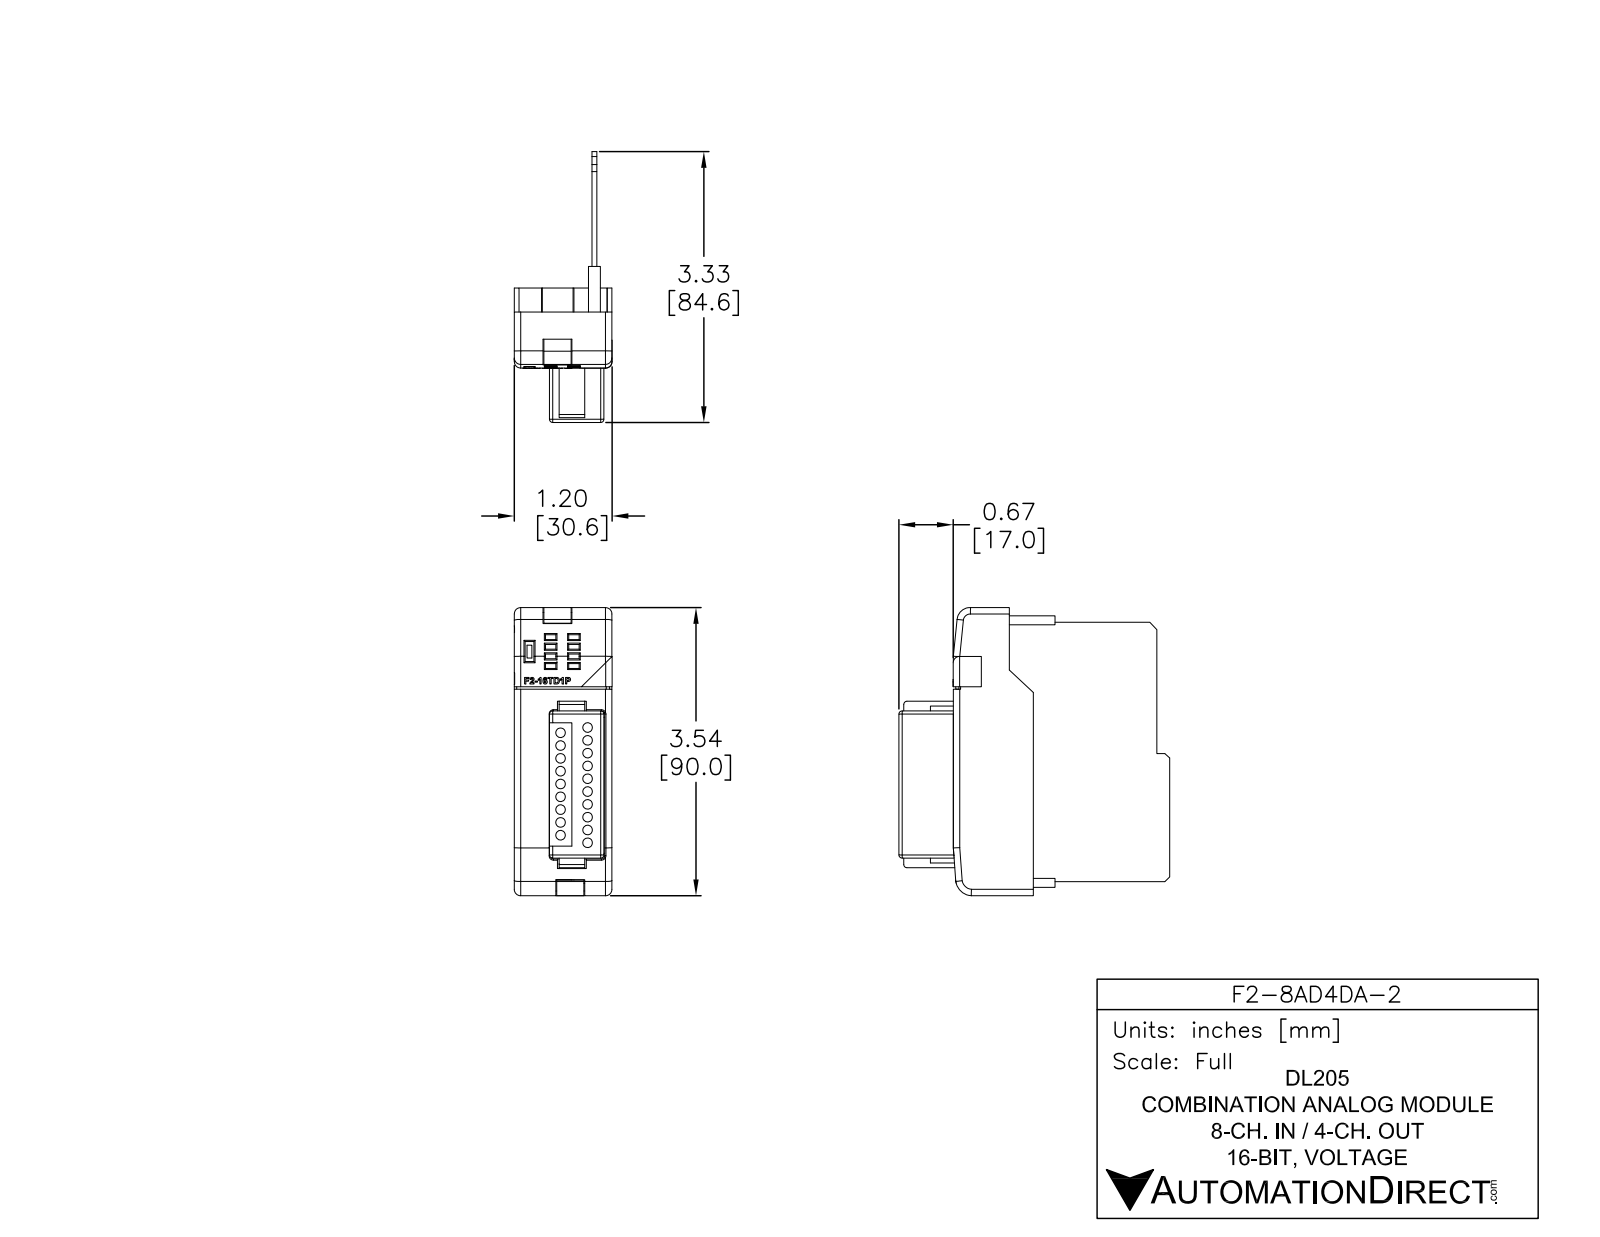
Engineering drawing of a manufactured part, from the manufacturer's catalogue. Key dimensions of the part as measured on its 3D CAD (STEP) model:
Part name (STEP PRODUCT): F2-8AD4DA-2
STEP written by: SolidWorks 2011 (AUTOMOTIVE_DESIGN)
Units: millimetres
Bodies: 2 solids, 618 faces (410 planar, 138 cylindrical, 70 other)
Overall size (bounding box): 90 × 84.6 × 30.55
Volume: 30 556 mm³ · Surface area: 32 608 mm²
Round holes (diameter × count): ⌀3 ×19
Partial cylindrical surfaces — rounded edges, fillets, slot ends (radius × count): R0.35 ×28, R1 ×18, R0.5 ×12, R2 ×11, R0.25 ×6, R2.62 ×1, R3.79 ×1, R4.12 ×1
Main face-to-face distances: 1.5, 4.72, 3.22, 6.22, 0.5, 1, 24.28, 29, 18, 11
Hole centre spacings: 4, 8, 12, 16, 8.61, 8.77, 20, 10.16
